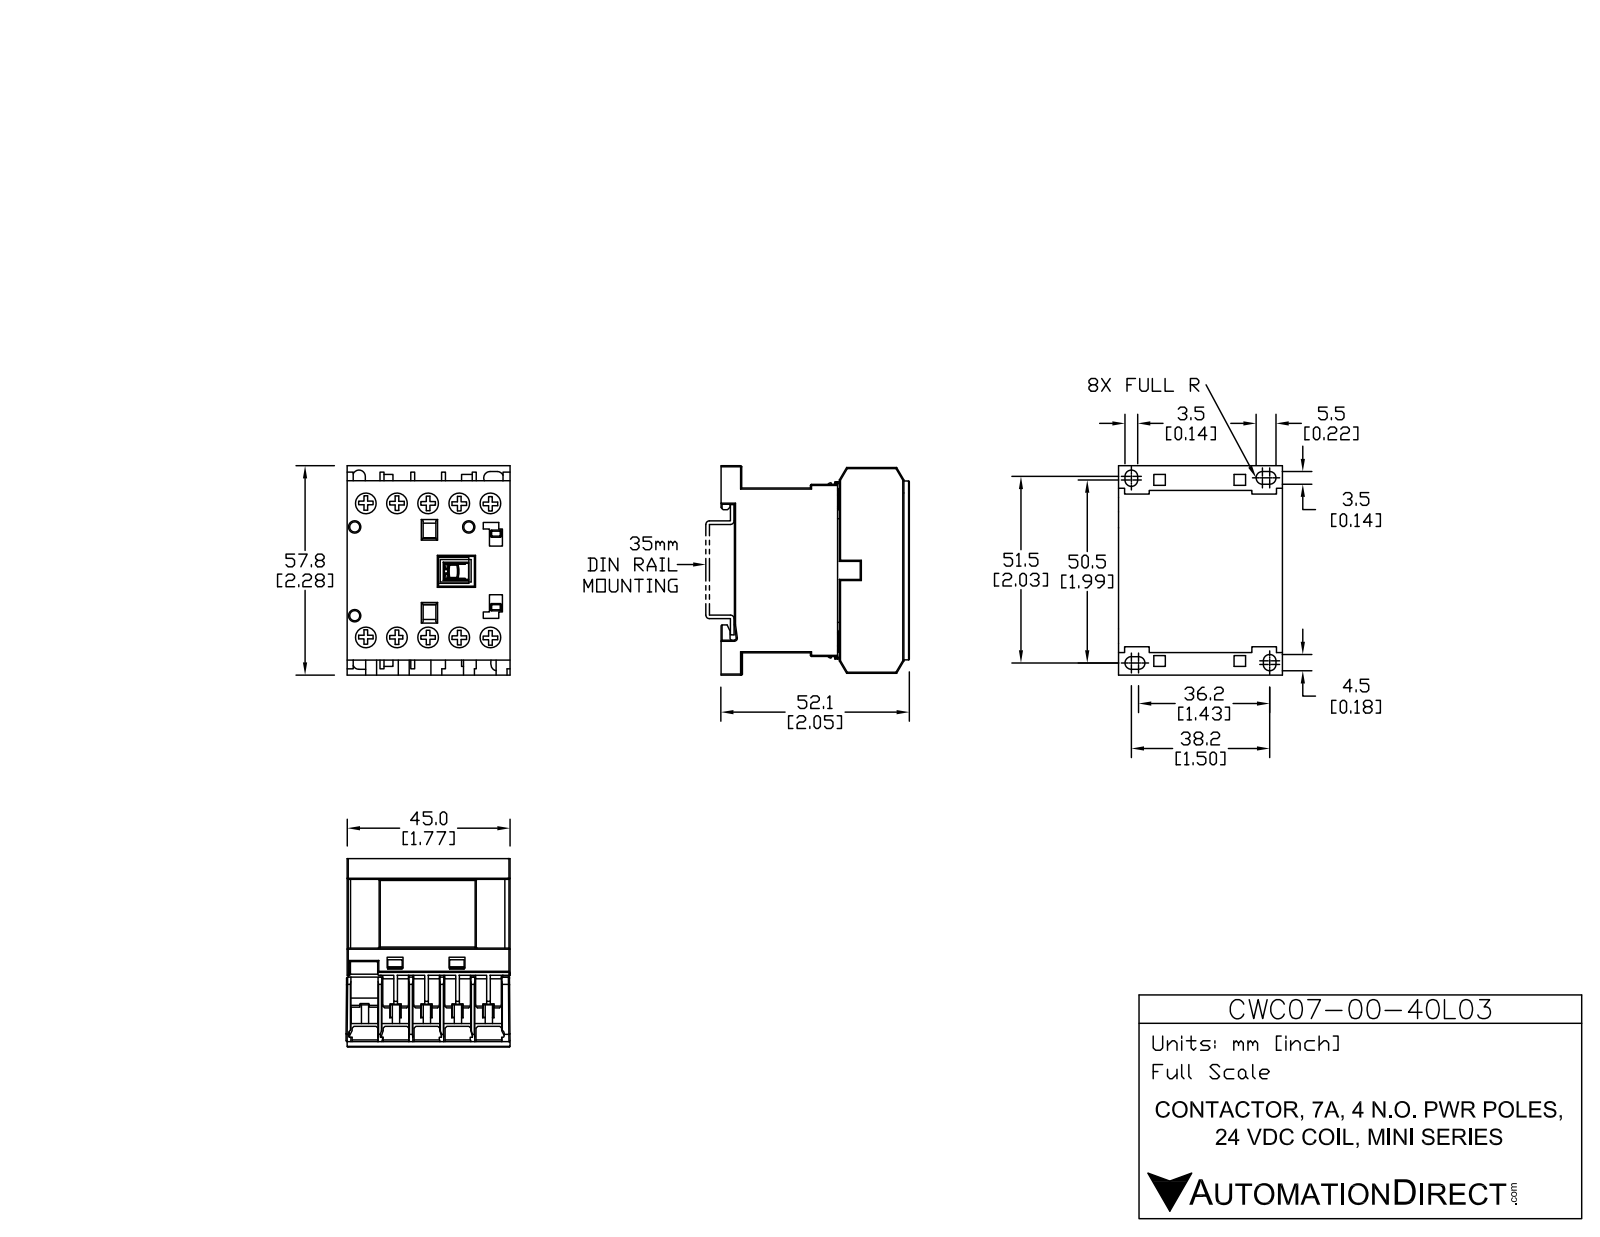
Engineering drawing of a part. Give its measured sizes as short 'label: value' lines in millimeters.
name: CWC07-00-40L03
written by: SolidWorks 2013 (AUTOMOTIVE_DESIGN)
unit: mm
bodies: 15 solids, 535 faces (445 planar, 90 cylindrical, 0 other)
size: 58.04 × 52.12 × 45.75
volume: 97 133 mm³; area: 30 437 mm²
holes: 10× ⌀6.2, 3× ⌀2.8
bosses: 10× ⌀5.9
rounds: 20× R0.3, 6× R1.72, 2× R1.73, 1× R0.32, 1× R0.42, 1× R0.55
face distances: 8.25, 45.5, 1.25, 16.5, 9.5, 5.5, 17.75, 5.13, 10.63, 7
hole spacings: 8.55, 37.94, 17.1, 40.72, 36.96, 25.65, 44.99, 6.91
